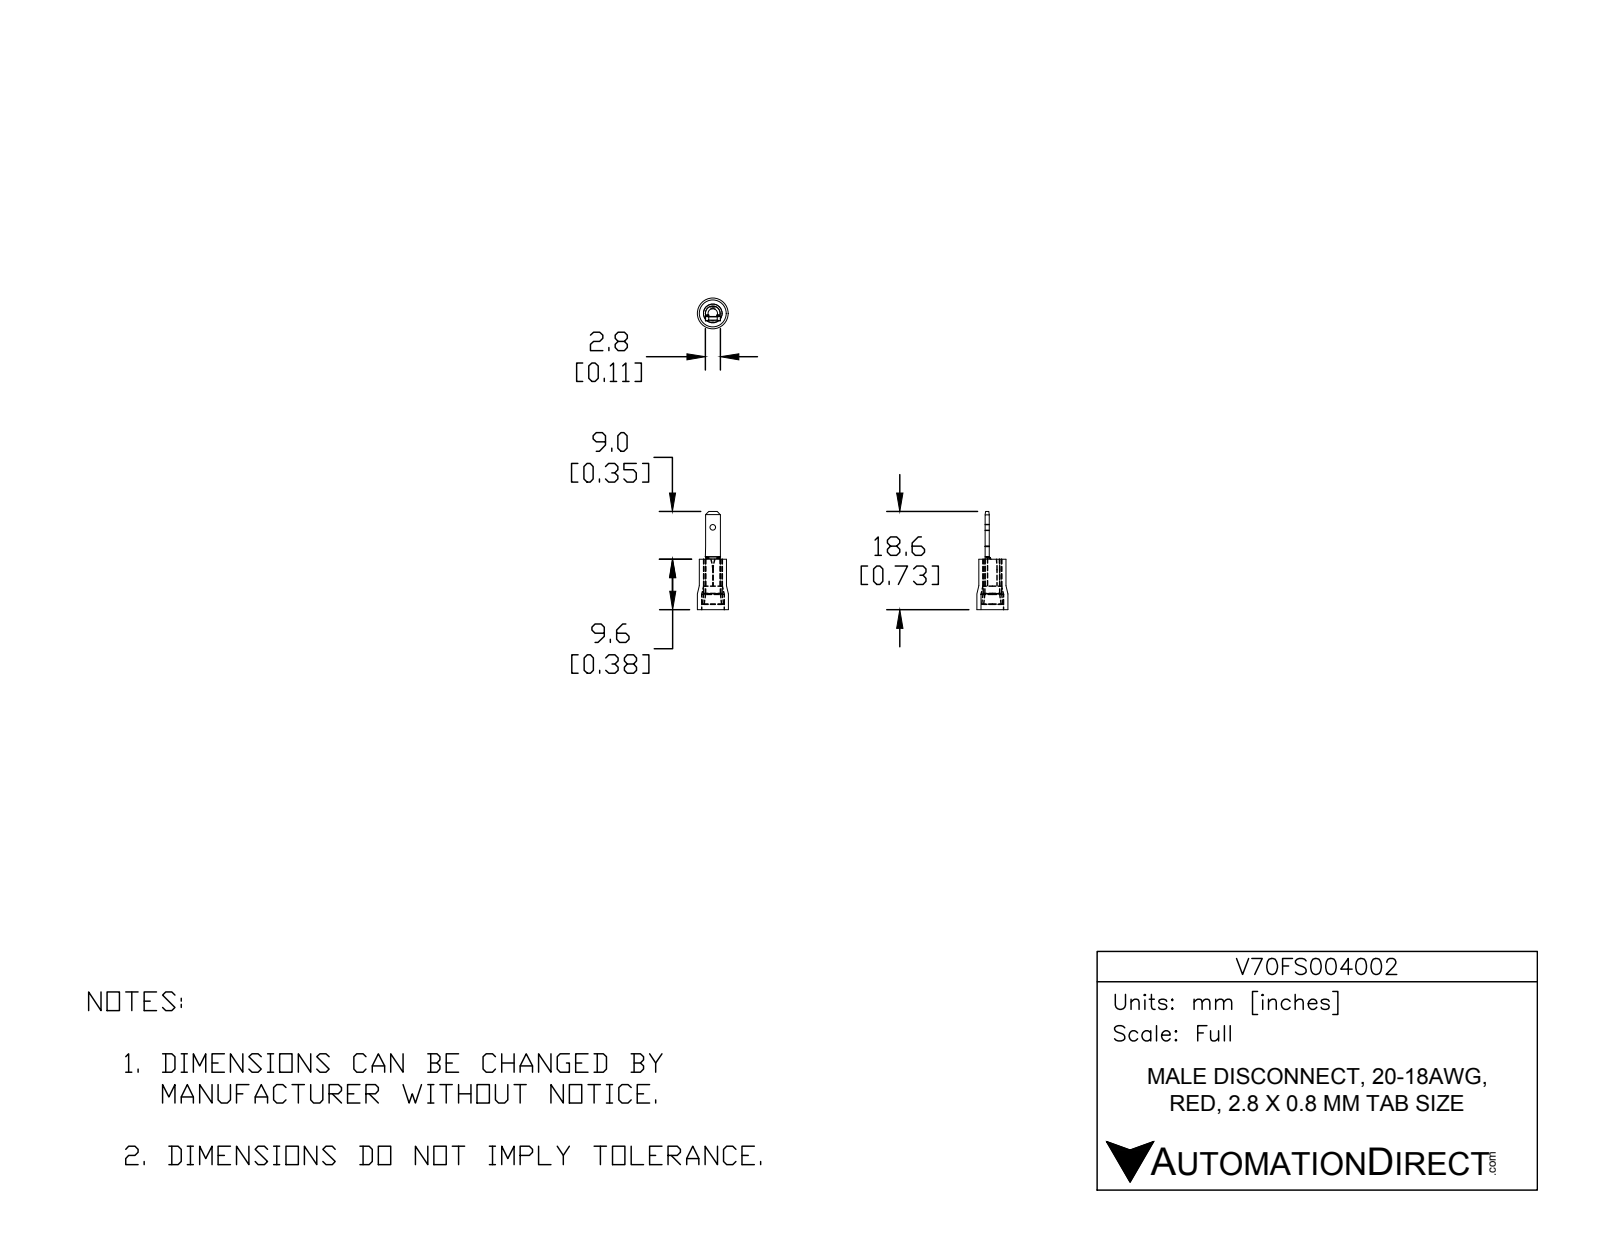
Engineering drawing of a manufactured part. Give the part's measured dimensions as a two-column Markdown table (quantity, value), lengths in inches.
| quantity | value |
| --- | --- |
| part name | V70FS004002 |
| STEP written by | SolidWorks 2017 (AUTOMOTIVE_DESIGN) |
| units | inches |
| bodies | 3 solids, 59 faces (19 planar, 22 cylindrical, 18 other) |
| overall size | 0.731 × 0.231 × 0.231 |
| volume | 0.011 in³ |
| surface area | 0.975 in² |
| round holes (diameter × count) | 0.043 × 1, 0.069 × 1, 0.11 × 1, 0.139 × 1, 0.168 × 1 |
| round bosses / shafts (diameter × count) | 0.231 × 1, 0.202 × 1, 0.138 × 1, 0.109 × 1 |
| partial cylindrical surfaces (radius × count) | 0.232 × 2 |
| main face-to-face distances | 0.031, 0.377, 0.11, 0.18, 0.197, 0.054, 0.056, 0.731, 0.551, 0.354 |
